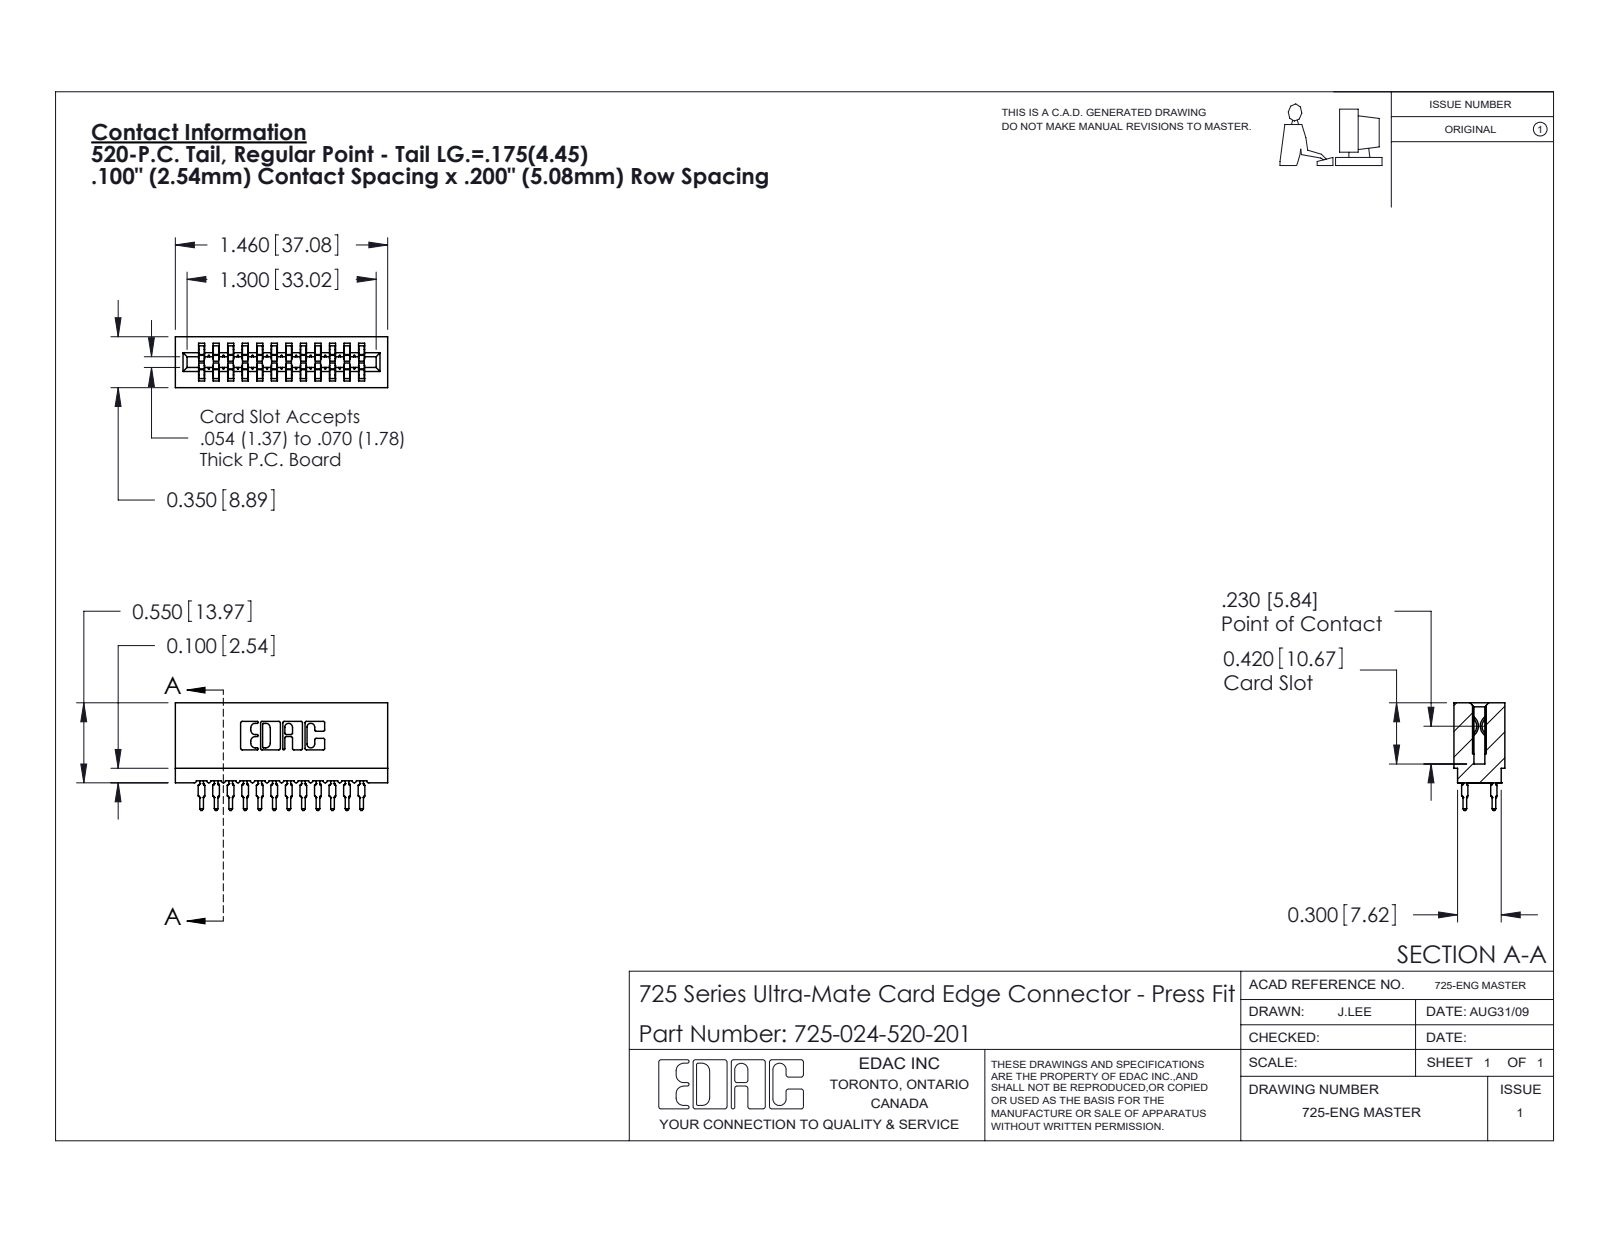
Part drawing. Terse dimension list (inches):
name: 745-292-001_520; 725-024-520-201; 725 Part_Insulator Option - 01
written by: SolidWorks 2020 (CONFIG_CONTROL_DESIGN)
unit: in
bodies: 25 solids, 2243 faces (1159 planar, 460 cylindrical, 624 other)
size: 1.46 × 0.741 × 0.35
volume: 0.187 in³; area: 8.904 in²
rounds: 48× R0.021, 24× R0.015, 22× R0.01, 8× R0.005, 8× R0.011, 6× R0.007, 6× R0.031, 3× R0.026
face distances: 0.1, 0.2, 0.3, 0.4, 0.5, 0.6, 0.258, 0.158, 0.058, 0.042
